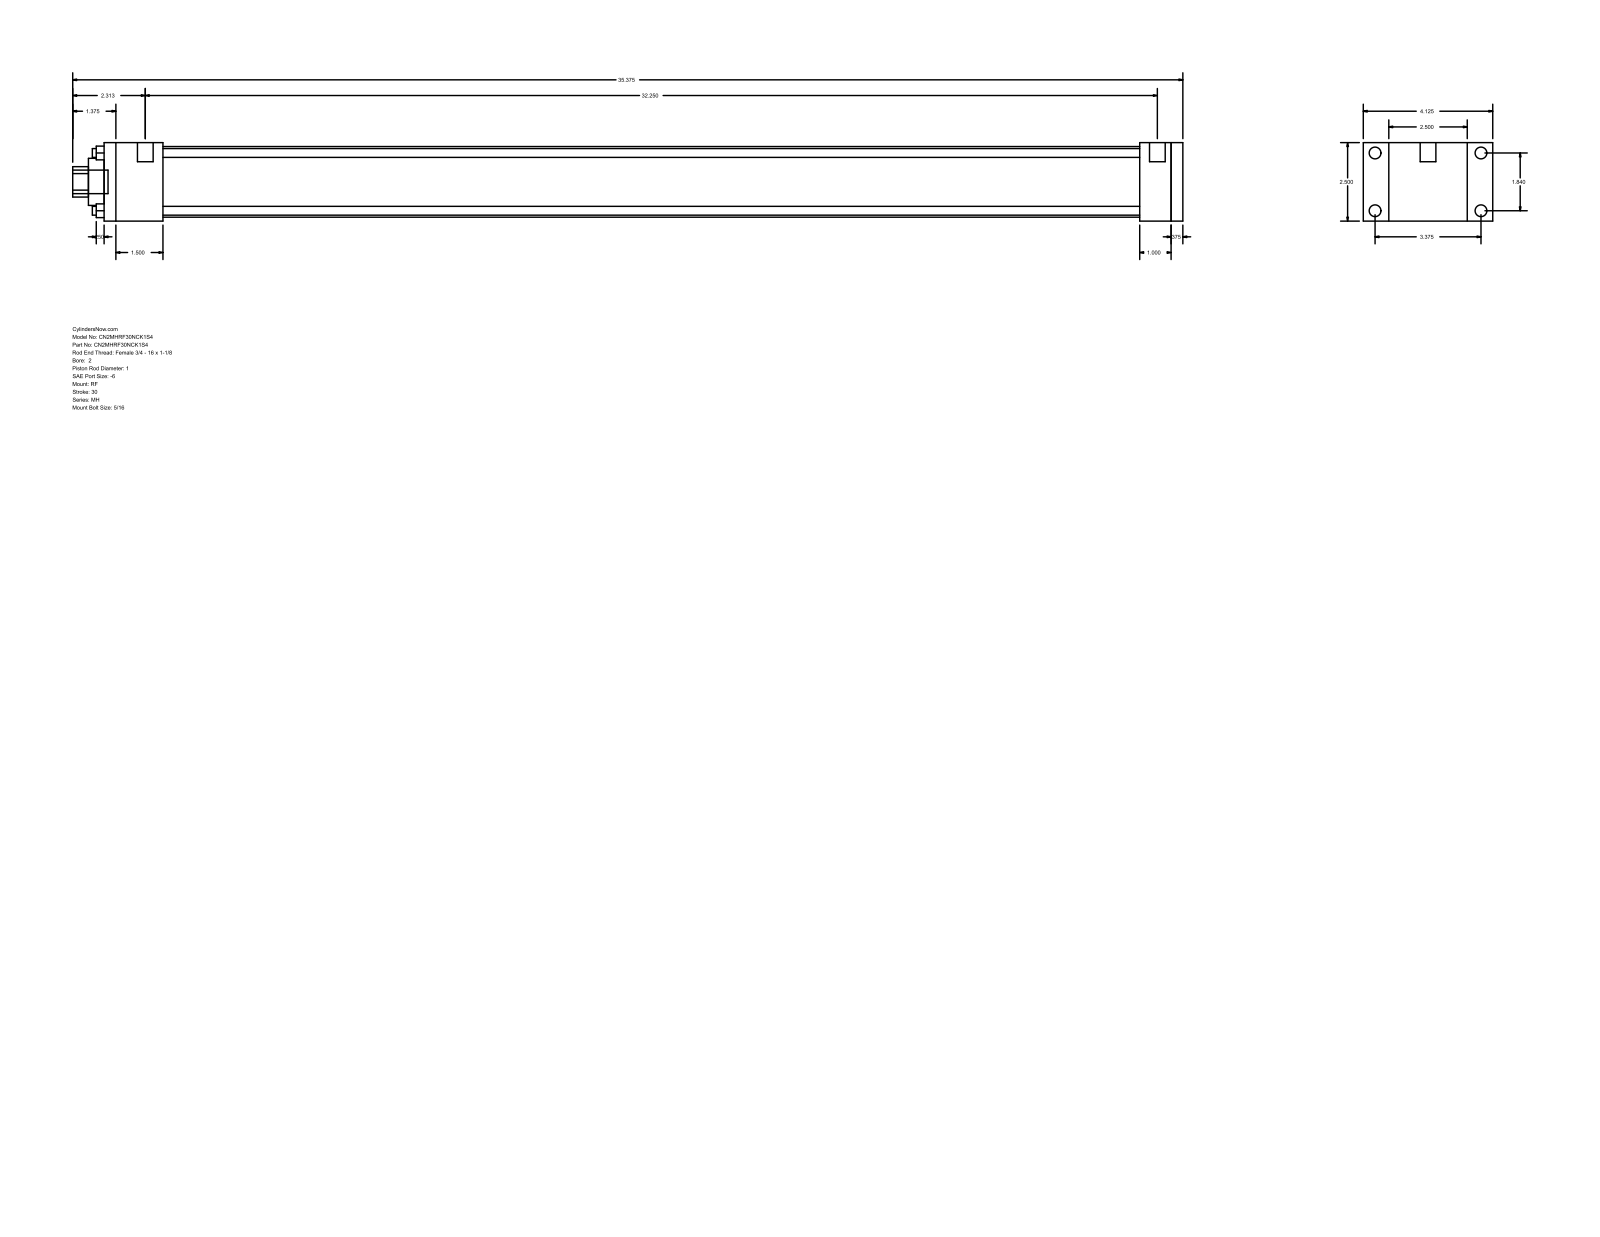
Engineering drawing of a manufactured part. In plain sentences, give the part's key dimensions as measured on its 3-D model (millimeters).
The part is named "MH_RF__0200_1". Its 3-D file was written by "GSSL Pune (CONFIG_CONTROL_DESIGN)". It is 0 solids with 92 faces: 64 planar, 28 cylindrical and 0 other. Overall it measures 898.52 by 104.78 by 63.5 millimeters. Round holes: 4 of diameter 7.14, 1 of diameter 25.4, 1 of diameter 38.1, 1 of diameter 57.15. Round bosses or shafts: 4 of diameter 9.53, 4 of diameter 5.56, 2 of diameter 12.7, 1 of diameter 19.05. Partial cylindrical surfaces (rounded edges, fillets, slot ends): 1 of radius 12.29. The main face-to-face distances are 63.5, 9.52, 873.12, 863.6, 20.64, 25.4, 47.63, 838.2, 790.57, 815.97. The hole center spacings are 33.05, 46.74, 66.1.
